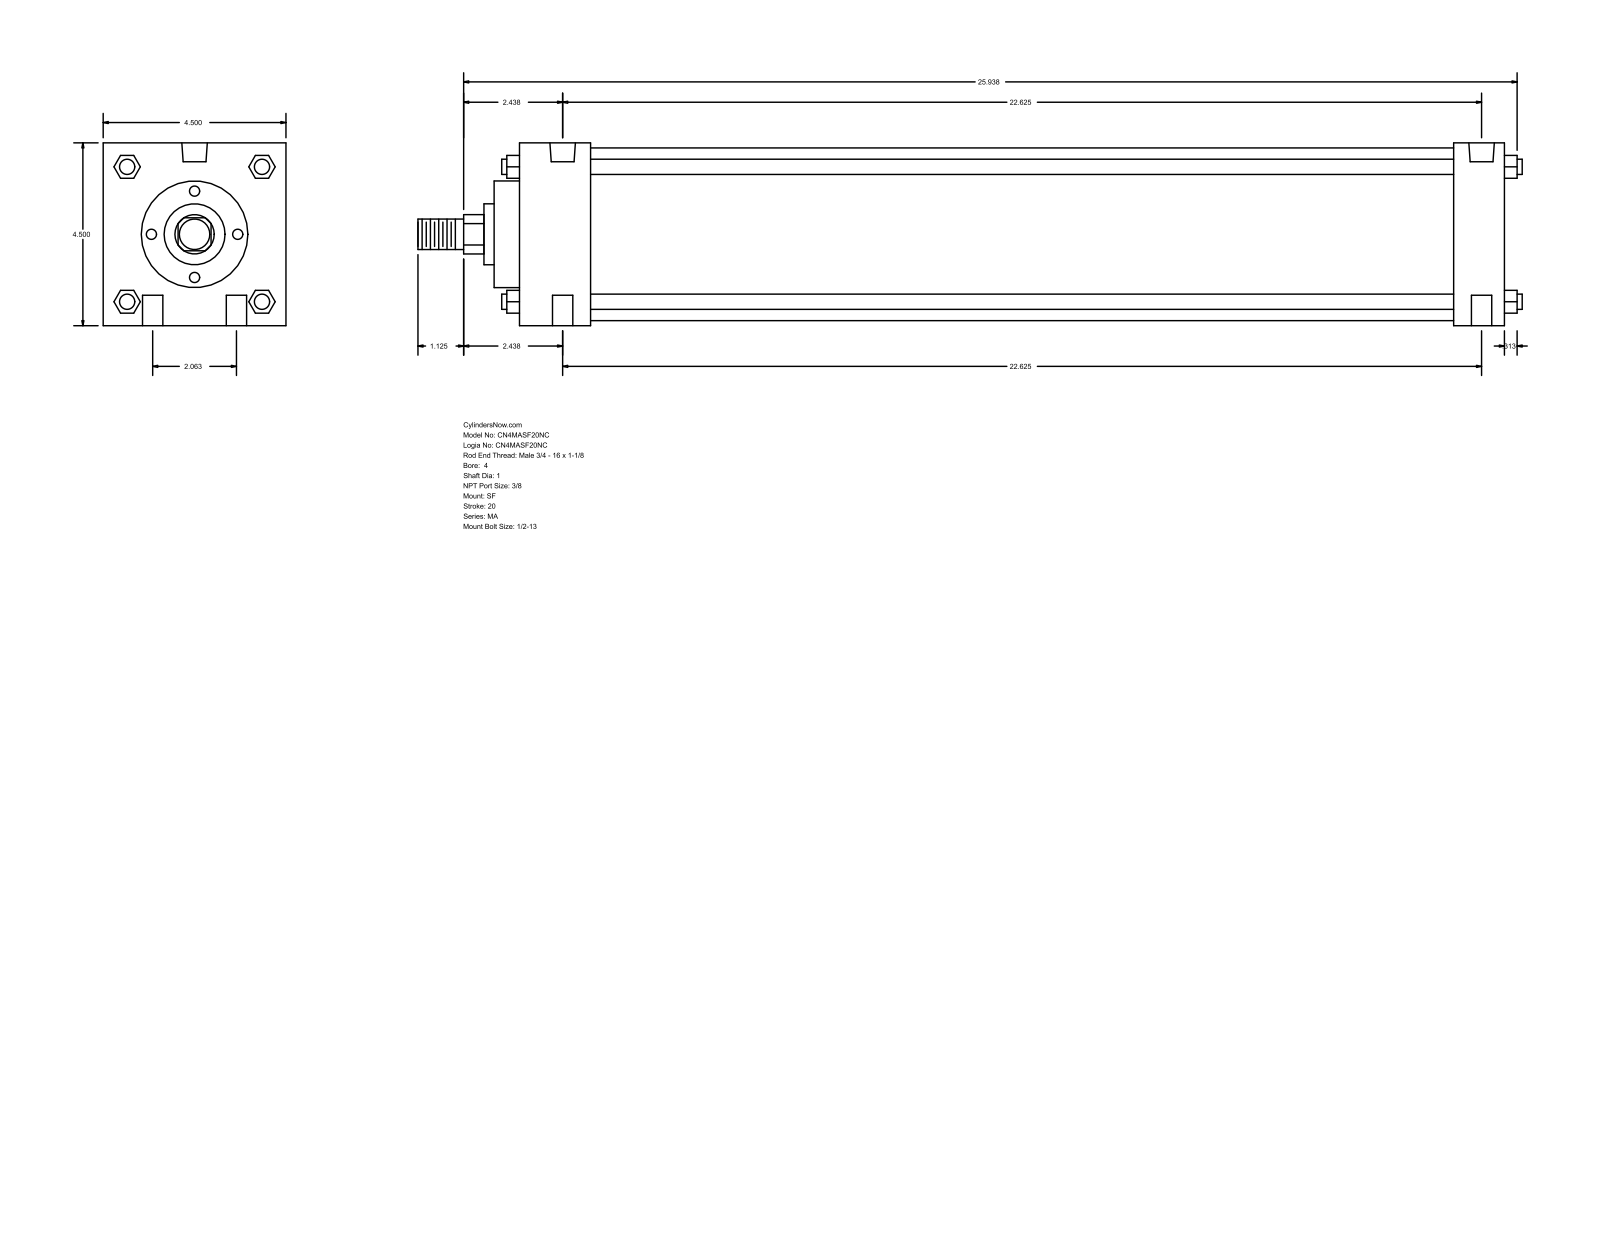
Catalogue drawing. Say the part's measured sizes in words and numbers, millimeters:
The part is named "MA_SF__0400_1". Its 3-D file was written by "GSSL Pune (CONFIG_CONTROL_DESIGN)". It is 0 solids with 126 faces: 95 planar, 31 cylindrical and 0 other. Overall it measures 690.56 by 114.3 by 114.3 millimeters. Round holes: 4 of diameter 12.7, 2 of diameter 11.11, 2 of diameter 15.93. Round bosses or shafts: 4 of diameter 9.53, 1 of diameter 107.95, 1 of diameter 66.67, 1 of diameter 38.1, 1 of diameter 25.4, 1 of diameter 19.05. Partial cylindrical surfaces (rounded edges, fillets, slot ends): 1 of radius 12.29. The main face-to-face distances are 114.3, 615.96, 584.2, 31.76, 44.46, 539.74, 571.5, 15.87, 60.33, 600.07. The hole center spacings are 26.19, 575.28, 574.68, 52.38, 577.06, 565.16.
